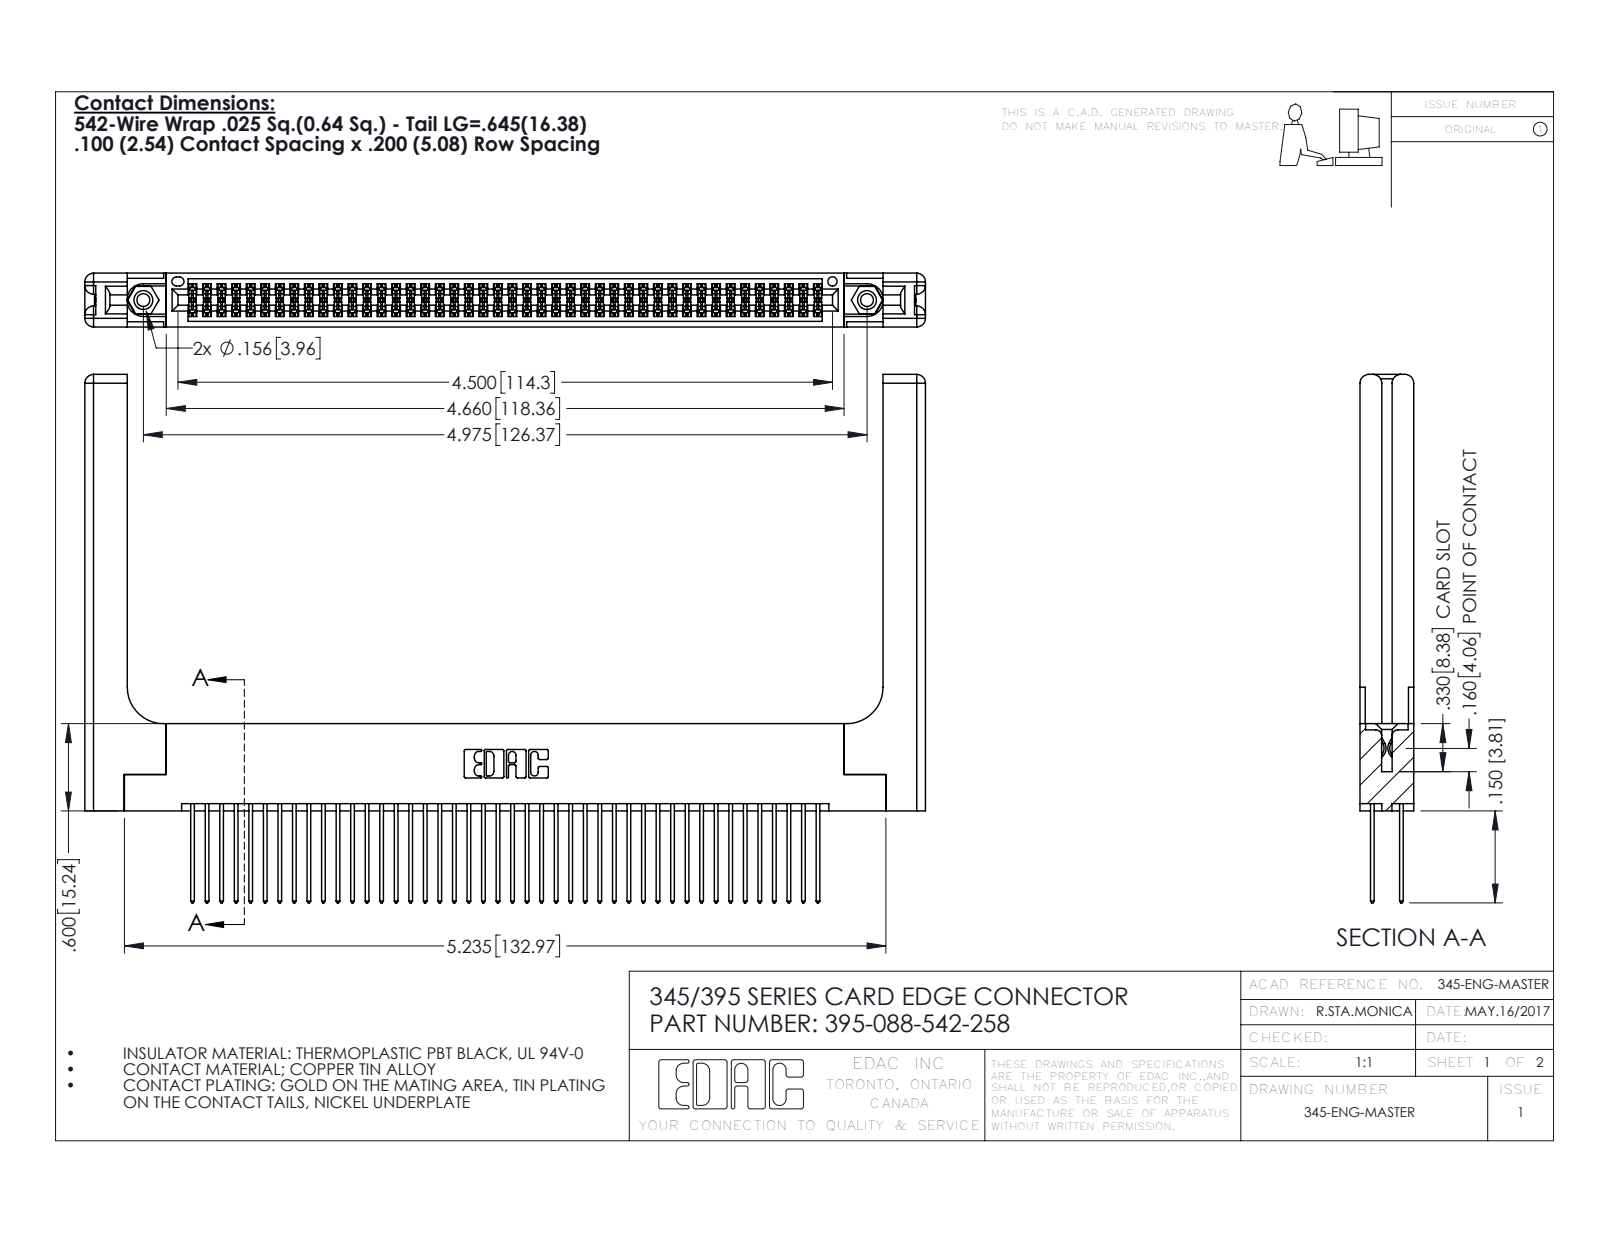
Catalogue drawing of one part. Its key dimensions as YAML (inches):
part_name: "345 Part_Flush Mounting Lugs - 0.156 Dia-TH; 395-088-542-258; 345-220-058_345-220-058; 345-292-001_345-293-142 (+1 more)"
step_written_by: "SolidWorks 2016 (CONFIG_CONTROL_DESIGN)"
units: inches
bodies: {solids: 93, faces: 4782, planar: 3132, cylindrical: 1590, other: 60}
overall_size: [5.779, 3.632, 0.37]
volume: 1.413
surface_area: 44.52
round_holes:
  - {diameter: 0.089, count: 2}
  - {diameter: 0.125, count: 2}
  - {diameter: 0.156, count: 2}
  - {diameter: 0.064, count: 1}
round_bosses_or_shafts:
  - {diameter: 0.155, count: 2}
partial_cylinders:
  - {radius: 0.006, count: 132}
  - {radius: 0.01, count: 88}
  - {radius: 0.01, count: 22}
  - {radius: 0.06, count: 16}
  - {radius: 0.007, count: 6}
  - {radius: 0.031, count: 6}
  - {radius: 0.026, count: 3}
  - {radius: 0.014, count: 2}
face_to_face_distances: [0.072, 0.298, 0.37, 0.2, 0.098, 0.272, 0.025, 0.225, 0.175, 0.148]
hole_center_spacings: [0.27, 4.739, 4.975]
